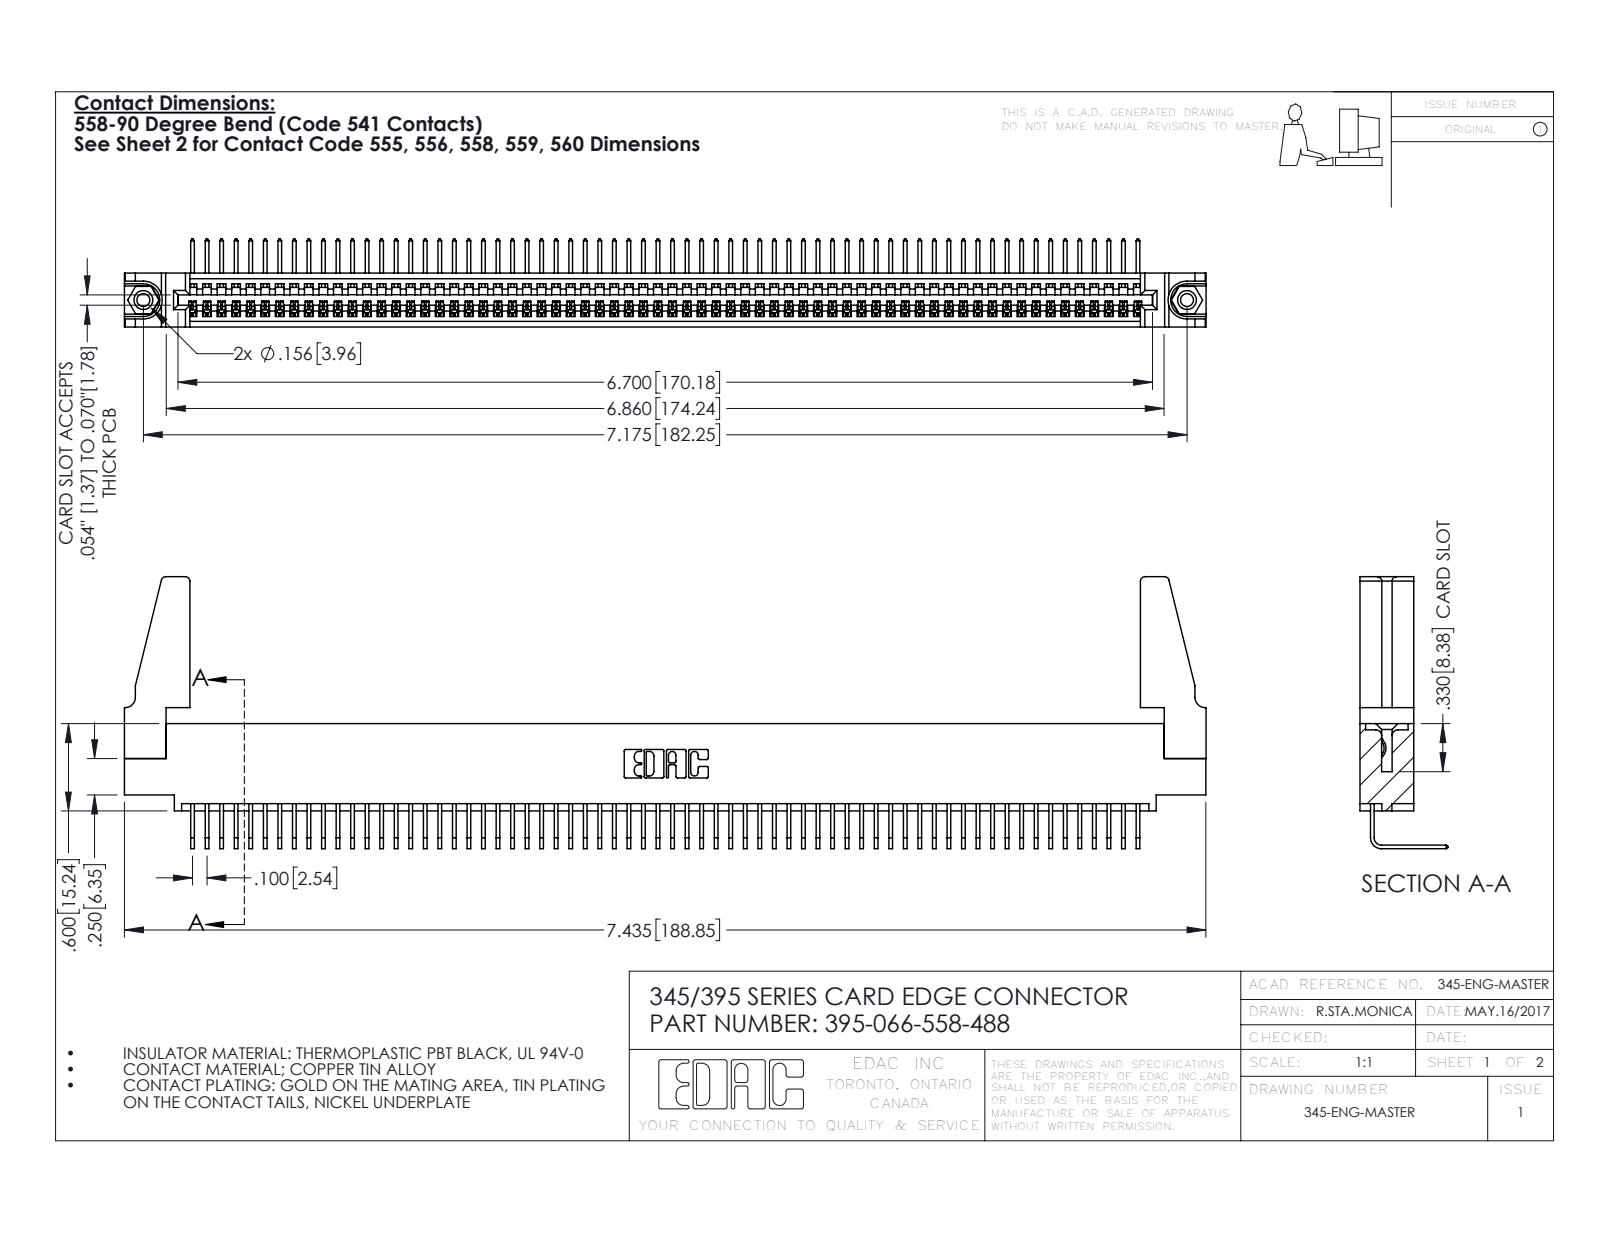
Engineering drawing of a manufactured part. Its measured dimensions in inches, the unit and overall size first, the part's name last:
Units: inches
Overall size (bounding box): 7.436 × 1.869 × 0.605
Round holes (diameter × count): ⌀0.089 ×2, ⌀0.125 ×2, ⌀0.156 ×2, ⌀0.064 ×1
Round bosses / shafts (diameter × count): ⌀0.155 ×2
Partial cylindrical surfaces — rounded edges, fillets, slot ends (radius × count): R0.006 ×132, R0.01 ×22, R0.03 ×8, R0.007 ×6, R0.031 ×6, R0.026 ×3, R0.031 ×2, R0.04 ×2
Main face-to-face distances: 0.072, 0.298, 0.37, 0.098, 0.272, 0.025, 0.2, 0.225, 0.149, 0.072
Hole centre spacings: 0.27, 6.939, 7.175
Volume: 1.314 in³ · Surface area: 45.14 in²
Bodies: 71 solids, 4214 faces (2928 planar, 1270 cylindrical, 16 other)
Part name (STEP PRODUCT): 345 Part_0.110 Offset - 0.156 Dia-TH; 345-220-078_345-220-088; 345-292-001_558 Tail - 2; 345-250-001_345-250-001-102 (+1 more)
STEP written by: SolidWorks 2016 (CONFIG_CONTROL_DESIGN)
